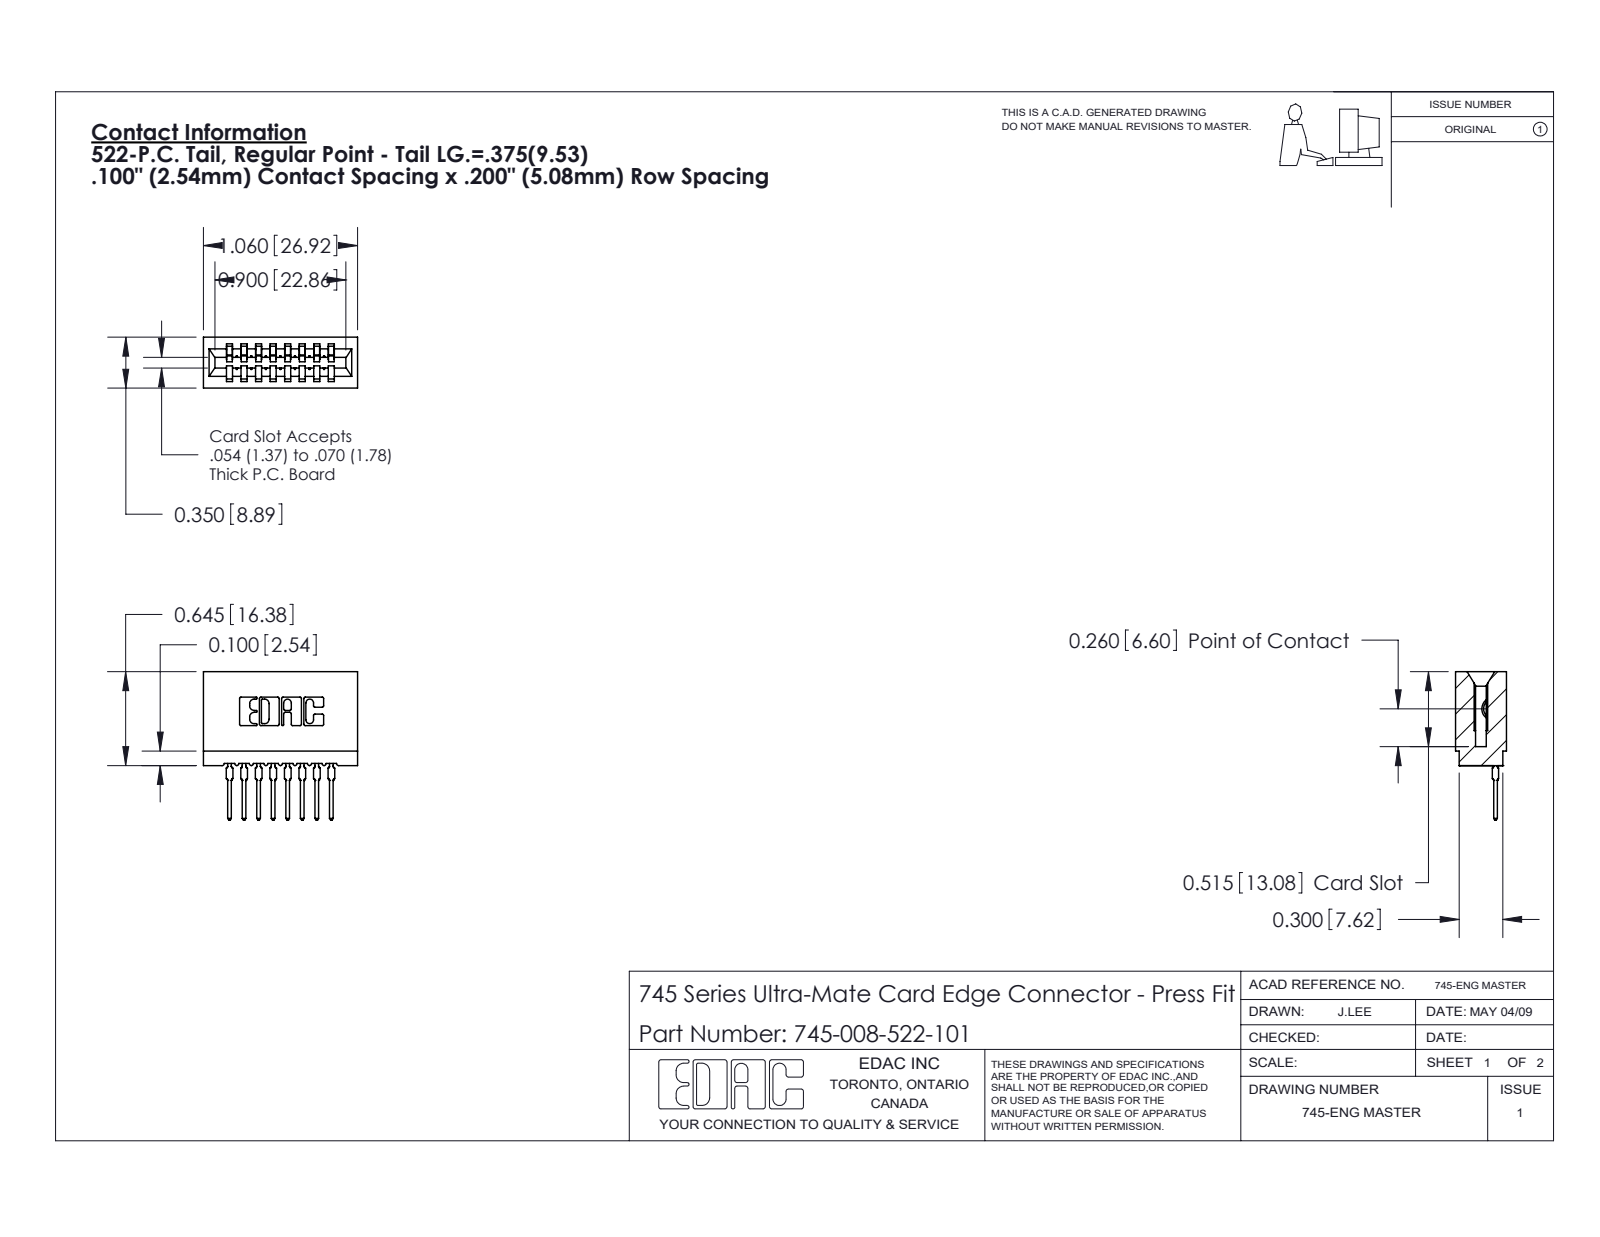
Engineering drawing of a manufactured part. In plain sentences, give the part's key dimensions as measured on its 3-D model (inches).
The part is named "745-292-001_522; 745-008-522-101; 745 Part_Insulator Option - 01". Its 3-D file was written by "SolidWorks 2020 (CONFIG_CONTROL_DESIGN)". It is 9 solids with 991 faces: 591 planar, 192 cylindrical and 208 other. Overall it measures 1.06 by 1.021 by 0.35 inches. Its volume is 0.156 cubic inches and its surface area 6.387 square inches. Partial cylindrical surfaces (rounded edges, fillets, slot ends): 22 of radius 0.01, 16 of radius 0.015, 16 of radius 0.021, 6 of radius 0.007, 6 of radius 0.031, 4 of radius 0.005, 4 of radius 0.011, 3 of radius 0.026. The main face-to-face distances are 0.1, 0.2, 0.3, 0.042, 0.4, 0.142, 0.058, 0.242, 0.5, 0.158.
